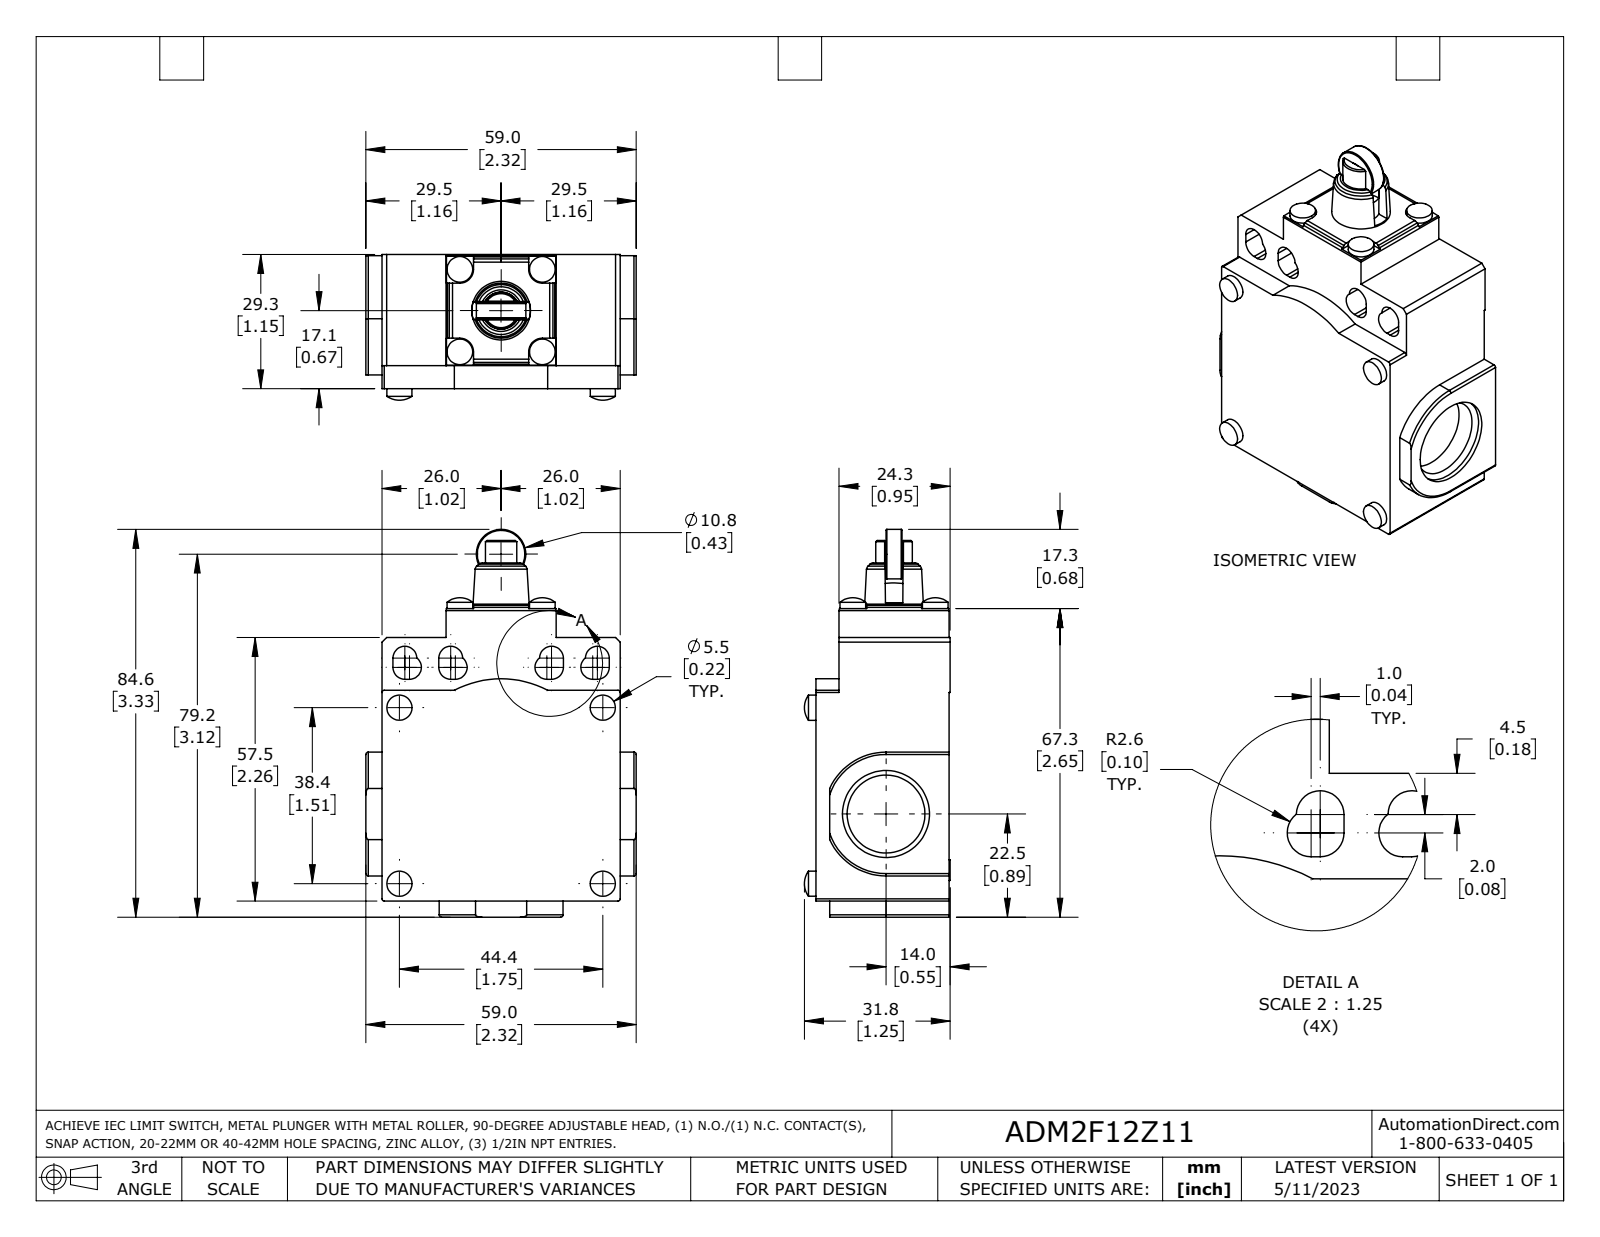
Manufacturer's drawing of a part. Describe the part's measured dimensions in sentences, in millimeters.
The part is named "ADM2F12Z11". Its 3-D file was written by "SolidWorks 2021 (AUTOMOTIVE_DESIGN)". It is 1 solid with 192 faces: 94 planar, 70 cylindrical and 28 other. Overall it measures 84.6 by 59 by 31.8 millimeters. Its volume is 88 770 cubic millimeters and its surface area 18 290 square millimeters. Round holes: 2 of diameter 17, 2 of diameter 19, 1 of diameter 8.1. Round bosses or shafts: 5 of diameter 5.6, 4 of diameter 5.5, 1 of diameter 10.8, 1 of diameter 8. Partial cylindrical surfaces (rounded edges, fillets, slot ends): 12 of radius 2.6, 10 of radius 0.5, 8 of radius 1, 4 of radius 3, 2 of radius 13.5, 1 of radius 10, 1 of radius 10.2, 1 of radius 20. The main face-to-face distances are 29.1, 3.5, 52, 6, 24, 2.5, 29.3, 55.5, 57.5, 49.5. The hole center spacings are 1.8.
